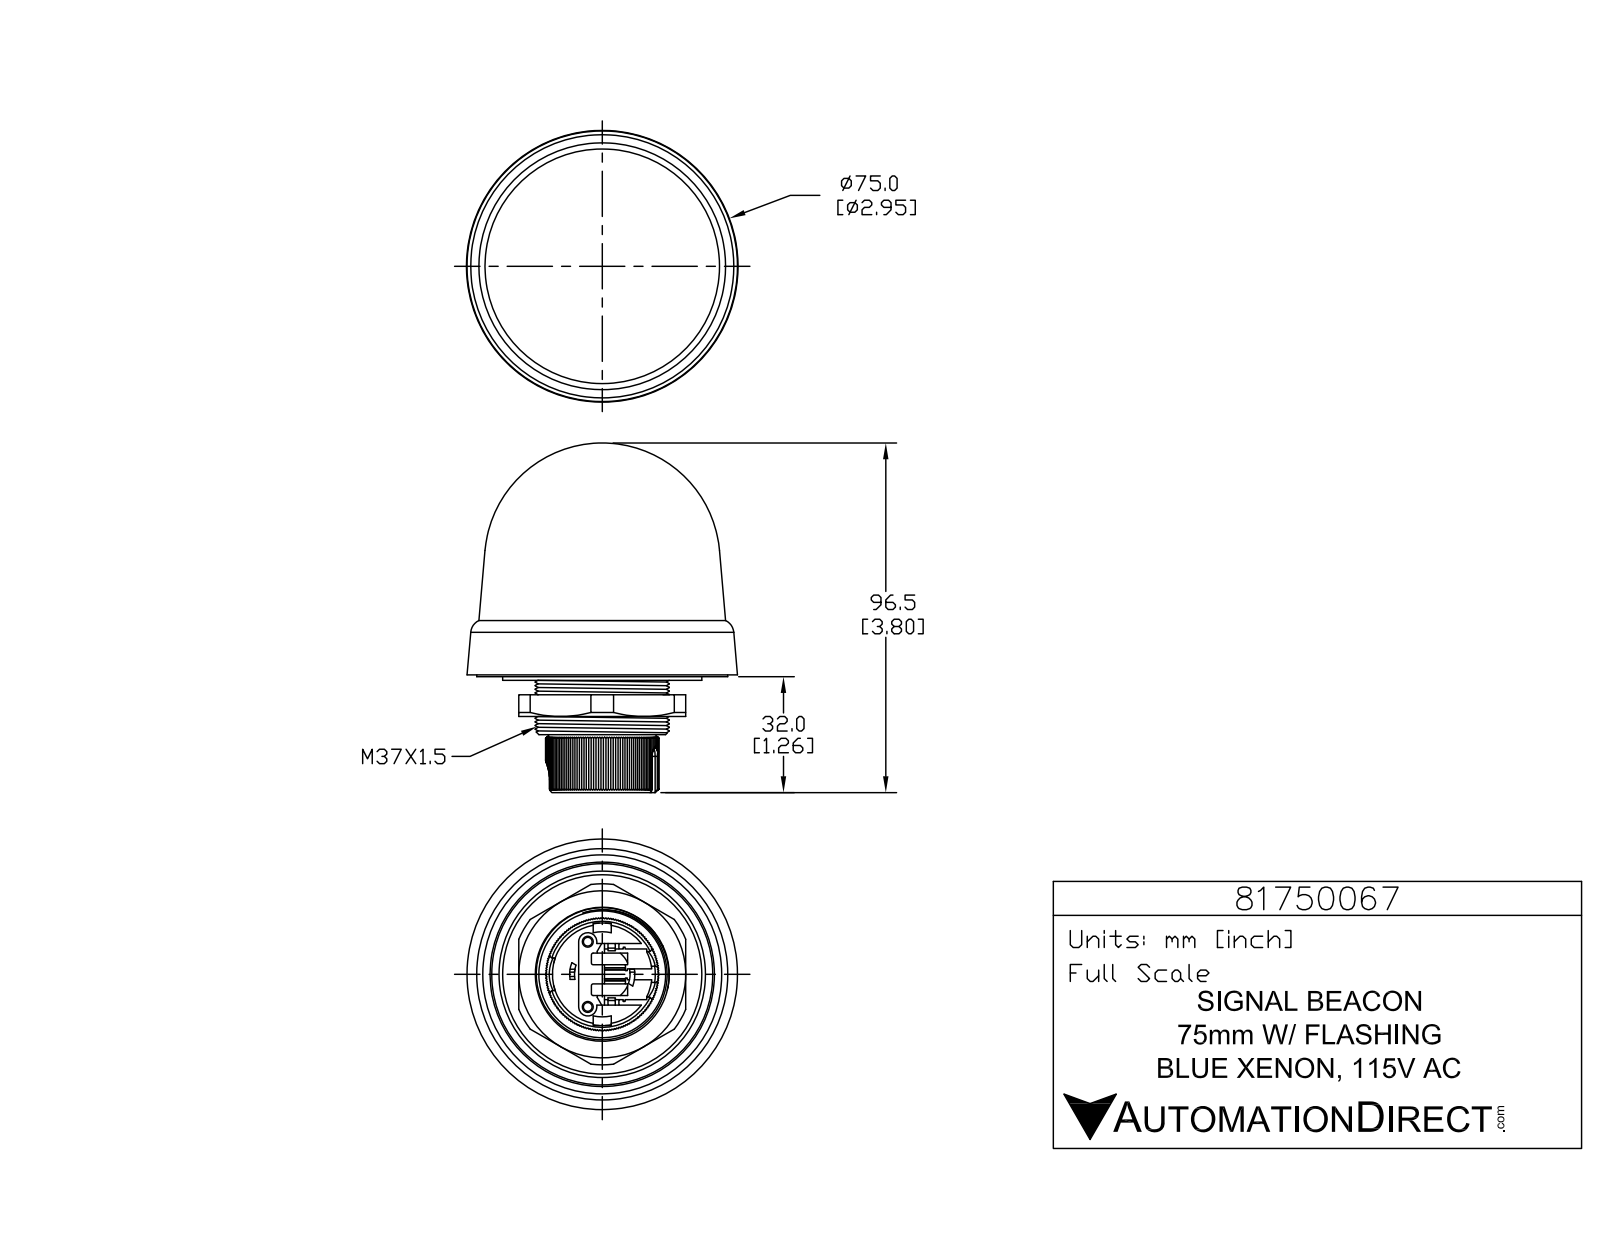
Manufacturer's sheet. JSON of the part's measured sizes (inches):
{"part_name": "81750067", "step_written_by": "SolidWorks 2019 (CONFIG_CONTROL_DESIGN)", "units": "inches", "bodies": {"solids": 3, "faces": 560, "planar": 432, "cylindrical": 80, "other": 48}, "overall_size": [3.799, 2.941, 2.941], "volume_in3": 12.36, "surface_area_in2": 58.68, "round_holes": [[0.094, 2], [0.118, 2], [0.604, 1], [1.142, 1]], "round_bosses_or_shafts": [[0.217, 2], [0.067, 2], [2.165, 1], [1.457, 1], [0.925, 1]], "partial_cylinders_radius": [[0.008, 6], [0.039, 6], [0.02, 4], [0.031, 2], [0.079, 2], [0.098, 2], [0.177, 1], [0.354, 1]], "face_to_face_distances": [0.177, 0.354, 0.197, 0.433, 0.512, 0.335, 0.059, 0.394, 0.118, 0.157], "hole_center_spacings": [0.388, 0.709]}
